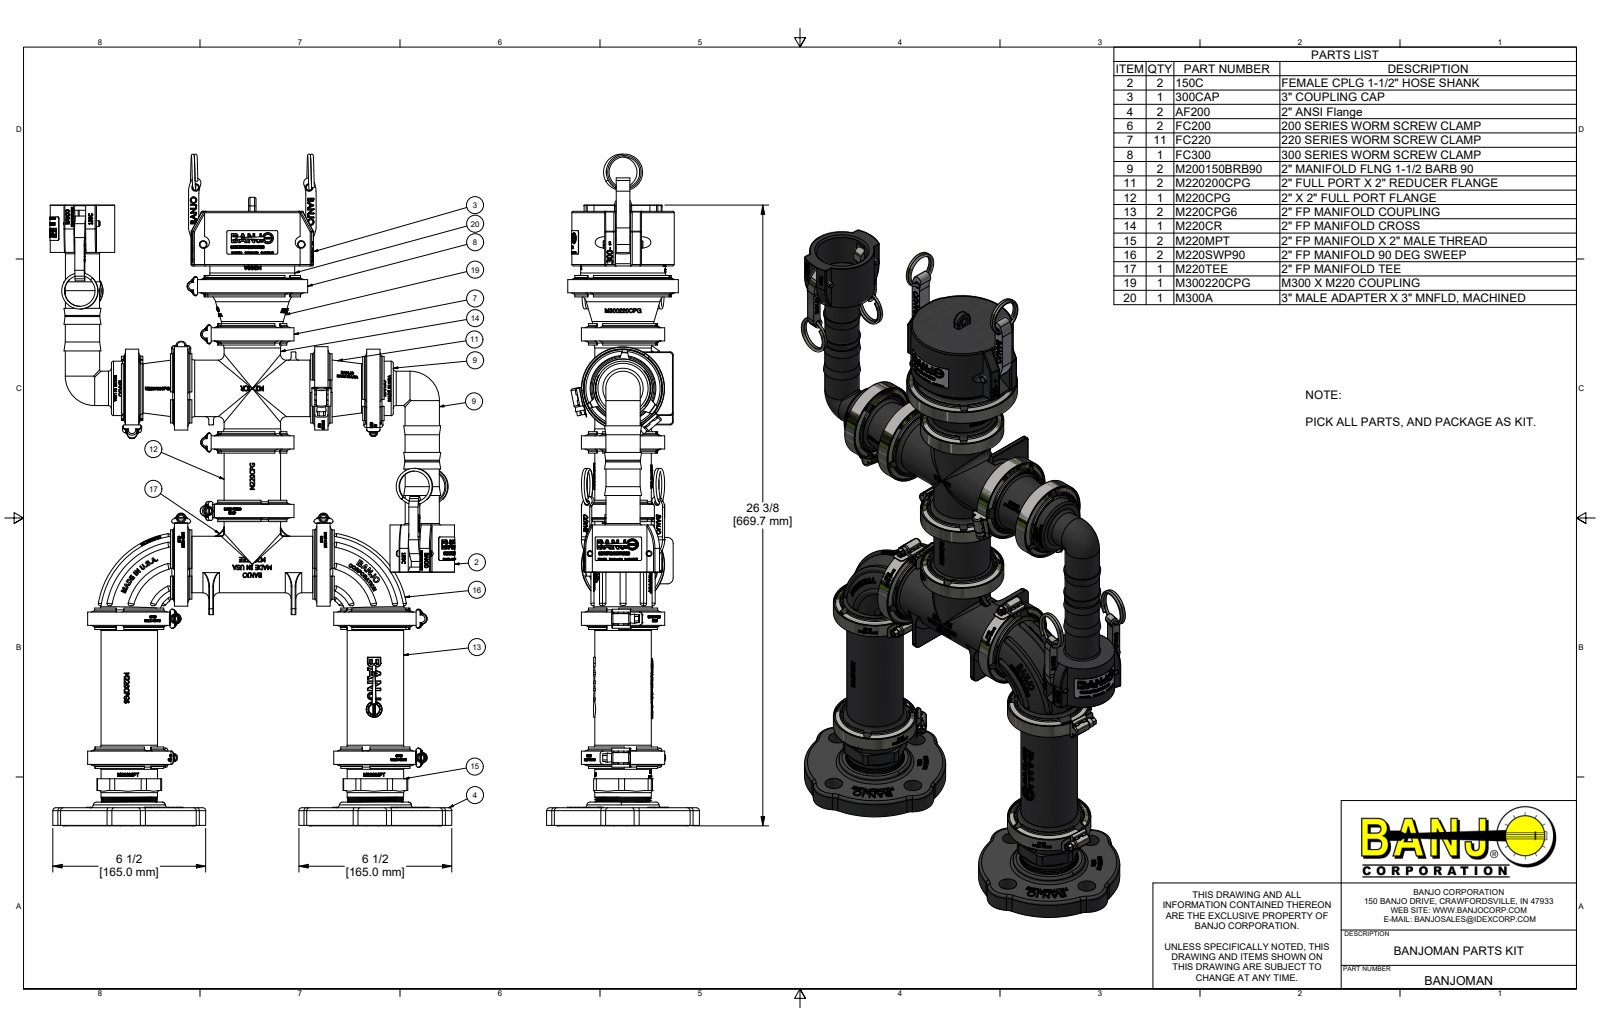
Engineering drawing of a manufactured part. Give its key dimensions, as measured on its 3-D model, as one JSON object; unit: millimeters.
{"part_name": "BANJOMAN; M220TEE; M220TEEUD; M220CPG (+8 more)", "step_written_by": "Autodesk Inventor 2022 (AUTOMOTIVE_DESIGN)", "units": "millimeters", "bodies": {"solids": 76, "faces": 19491, "planar": 8302, "cylindrical": 2602, "other": 8587}, "overall_size": [724.7, 437.1, 165], "volume_mm3": 3495000, "surface_area_mm2": 1420000, "round_holes": [[6.4, 20], [19.1, 8], [50.8, 5], [55.9, 5], [66.8, 5], [72.1, 5], [86.4, 5], [88.9, 5], [5, 4], [6.6, 4], [66.5, 4], [8.1, 3]], "round_bosses_or_shafts": [[89.9, 5], [83.1, 5], [74.6, 5], [66.3, 5], [61, 5], [6.6, 4], [6.3, 4], [37.1, 3]], "partial_cylinders_radius": [[0.2, 235], [0.8, 106], [1.5, 104], [3.2, 66], [0.1, 34], [12.7, 20], [6.4, 18], [5.6, 14]], "face_to_face_distances": [2.5, 205.2, 5.1, 19.1, 202.7, 53.8, 151.4, 31.2, 120.1, 3.8], "hole_center_spacings": [60.3, 55.3, 85.3, 85.3, 90.1, 265.7, 10.1, 50.5]}
